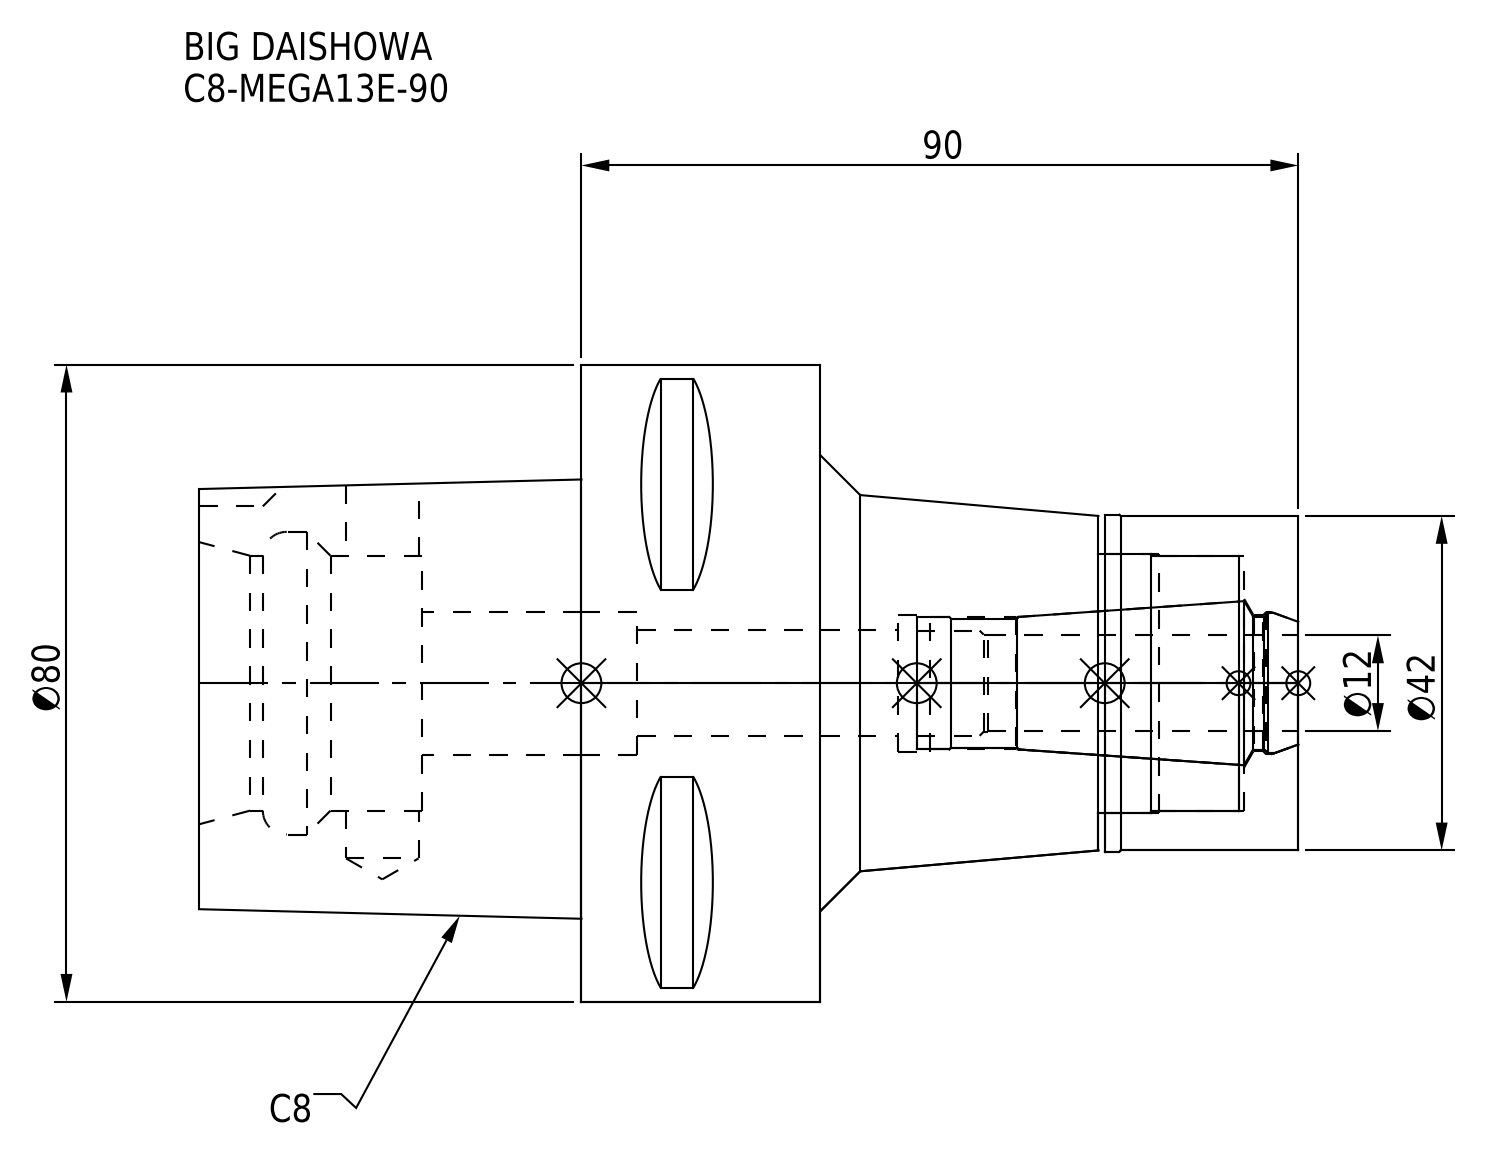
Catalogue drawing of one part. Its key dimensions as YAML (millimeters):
part_name: "C8-MEGA13E-90; C8-MEGA13E-90-120.stp; C8-MEGA13E-90-120-FreeParts; C8-MEGA13E-90-120_ASM.stp (+3 more)"
step_written_by: "SolidWorks 2019 (CONFIG_CONTROL_DESIGN)"
units: millimeters
bodies: {solids: 2, faces: 97, planar: 36, cylindrical: 37, other: 24}
overall_size: [138, 80, 80]
volume: 297496
surface_area: 48114
round_holes:
  - {diameter: 9.1, count: 1}
  - {diameter: 13.3, count: 1}
  - {diameter: 16.6, count: 1}
  - {diameter: 17, count: 1}
  - {diameter: 17.2, count: 1}
  - {diameter: 17.9, count: 1}
  - {diameter: 18, count: 1}
  - {diameter: 32, count: 1}
  - {diameter: 32.5, count: 1}
  - {diameter: 38, count: 1}
round_bosses_or_shafts:
  - {diameter: 80, count: 1}
  - {diameter: 42.3, count: 1}
  - {diameter: 42, count: 1}
partial_cylinders:
  - {radius: 6, count: 1}
face_to_face_distances: [30, 60, 90, 138, 78, 48, 25.1, 24.3, 35.7, 65.7]
